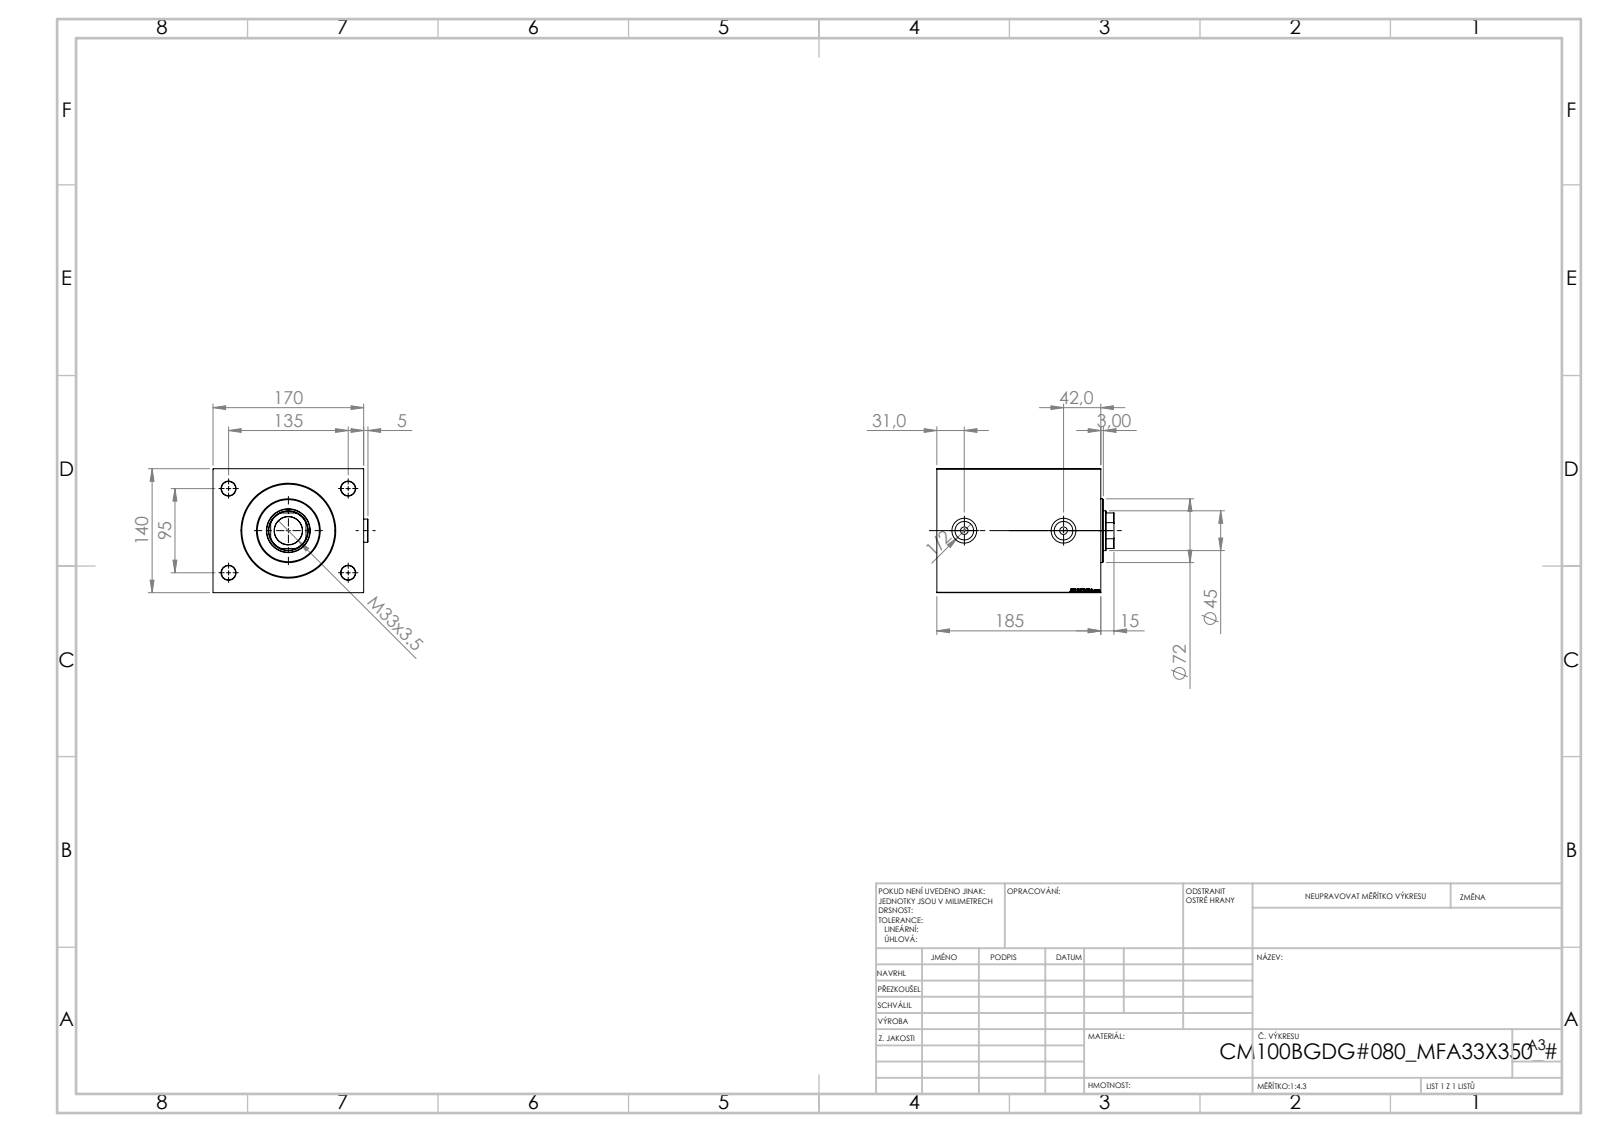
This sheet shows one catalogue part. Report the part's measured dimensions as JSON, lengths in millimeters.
{"part_name": "V450CM_B_VCP; V450CM_B_Body; V450CM_VC_B; Zatka_OIL_PORT", "step_written_by": "SolidWorks 2019 (CONFIG_CONTROL_DESIGN)", "units": "millimeters", "bodies": {"solids": 5, "faces": 938, "planar": 436, "cylindrical": 72, "other": 430}, "overall_size": [200, 174.9, 140], "volume_mm3": 3830000, "surface_area_mm2": 309999, "round_holes": [[16, 4], [8.5, 2], [20.96, 2], [28, 2], [31.5, 1], [45, 1], [48.5, 1], [49.5, 1], [100, 1], [102, 1], [105, 1]], "round_bosses_or_shafts": [[26, 2], [72, 1]], "partial_cylinders_radius": [[22, 1]], "face_to_face_distances": [170, 140, 185, 159, 26, 90, 15, 144, 64, 95], "hole_center_spacings": [82.54, 95, 135, 165.08, 112]}
